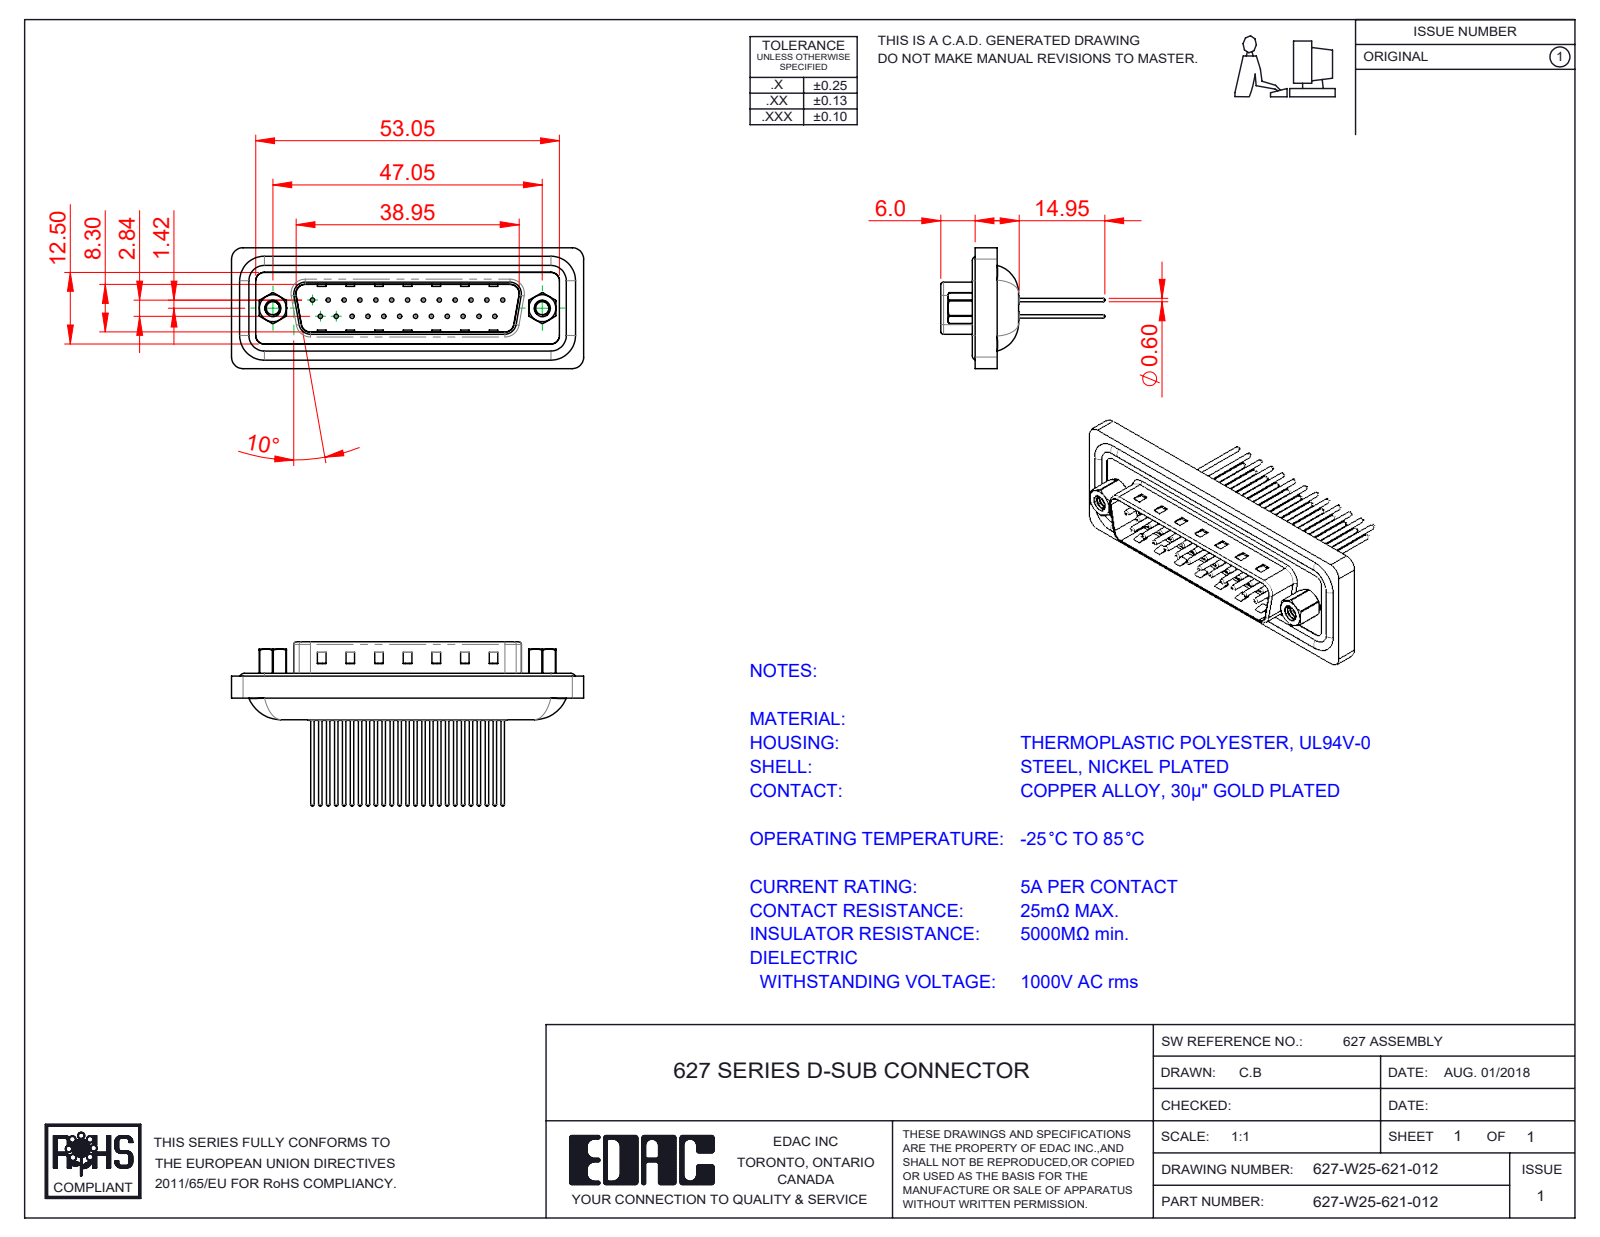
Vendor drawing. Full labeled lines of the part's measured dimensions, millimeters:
Part name (STEP PRODUCT): 627W Shell Front_25 Contacts; 627-W25-621-012; 627W Housing_25 Contacts; 627W Contact Row 1_21 (+4 more)
STEP written by: SolidWorks 2020 (CONFIG_CONTROL_DESIGN)
Units: millimetres
Bodies: 33 solids, 1495 faces (380 planar, 620 cylindrical, 495 other)
Overall size (bounding box): 61.5 × 28.65 × 21.1
Volume: 7 552 mm³ · Surface area: 11 602 mm²
Round holes (diameter × count): ⌀0.75 ×25, ⌀1.5 ×25, ⌀1.6 ×25, ⌀2 ×25, ⌀2.26 ×2, ⌀2.29 ×2, ⌀4 ×2, ⌀4.8 ×2, ⌀5 ×2
Round bosses / shafts (diameter × count): ⌀0.6 ×25, ⌀1.5 ×7, ⌀1.6 ×4, ⌀4.9 ×2, ⌀2.79 ×2
Partial cylindrical surfaces — rounded edges, fillets, slot ends (radius × count): R2 ×16, R1.5 ×14, R0.5 ×8, R2.7 ×6, R0.9 ×4, R1.6 ×4, R4.3 ×4, R0.4 ×2
Main face-to-face distances: 0.75, 0.4, 1.1, 2.75, 3.75, 4.6, 4.1, 0.5, 5.65, 15.45
Hole centre spacings: 3.16, 2.77, 5.54, 8.31, 11.08, 13.85, 5.04, 16.62
